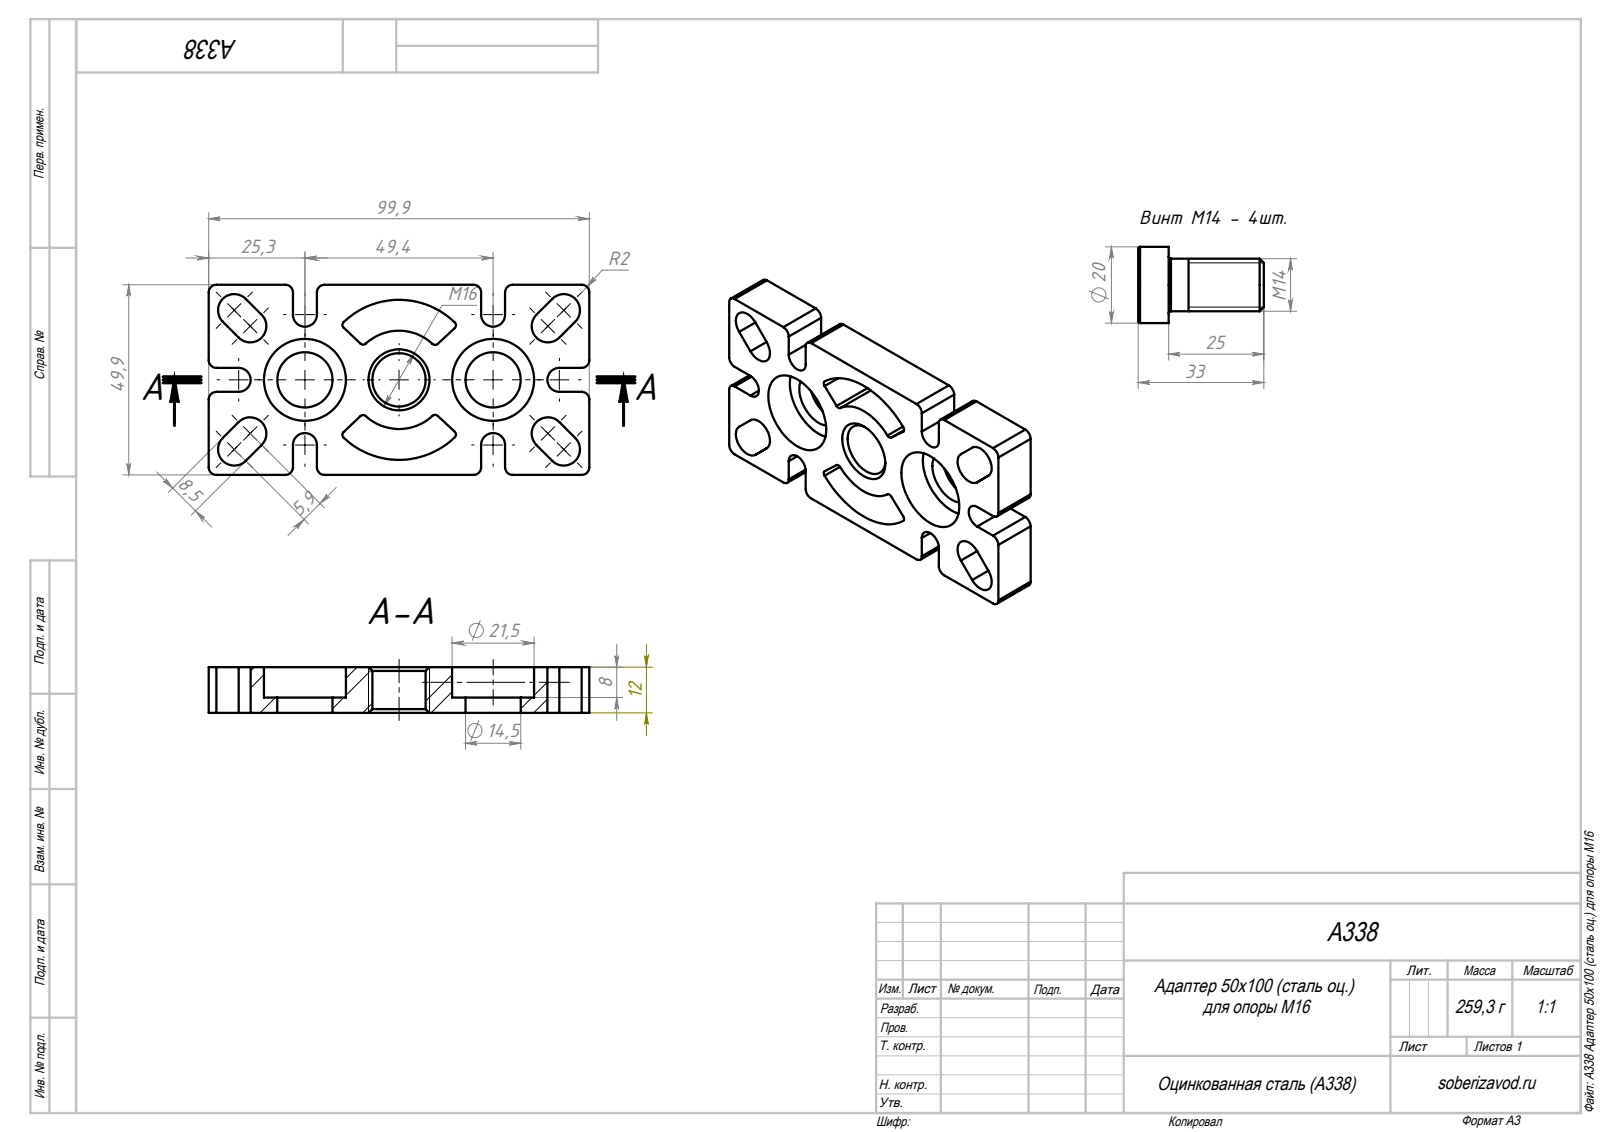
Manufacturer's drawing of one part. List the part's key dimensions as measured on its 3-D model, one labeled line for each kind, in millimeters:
Part name (STEP PRODUCT): A338 Адаптер 50х100 (сталь оц.) для опоры М16_00; A338 Адаптер 50х100 (сталь оц.) для опоры М16
STEP written by: SolidWorks 2018 (AUTOMOTIVE_DESIGN)
Units: millimetres
Bodies: 3 solids, 147 faces (60 planar, 71 cylindrical, 16 other)
Overall size (bounding box): 99.9 × 49.9 × 33
Volume: 46 874 mm³ · Surface area: 21 706 mm²
Round holes (diameter × count): ⌀6 ×2, ⌀14.5 ×2, ⌀21.5 ×2, ⌀14 ×1
Round bosses / shafts (diameter × count): ⌀21 ×2, ⌀14 ×2
Partial cylindrical surfaces — rounded edges, fillets, slot ends (radius × count): R2 ×16, R1 ×8, R4.25 ×8, R3.15 ×6, R12.9 ×1, R21 ×1
Main face-to-face distances: 12, 49.9, 4, 8, 99.9, 6.3, 49.4, 22.1, 28.4, 71.5
Hole centre spacings: 24.7, 49.4
